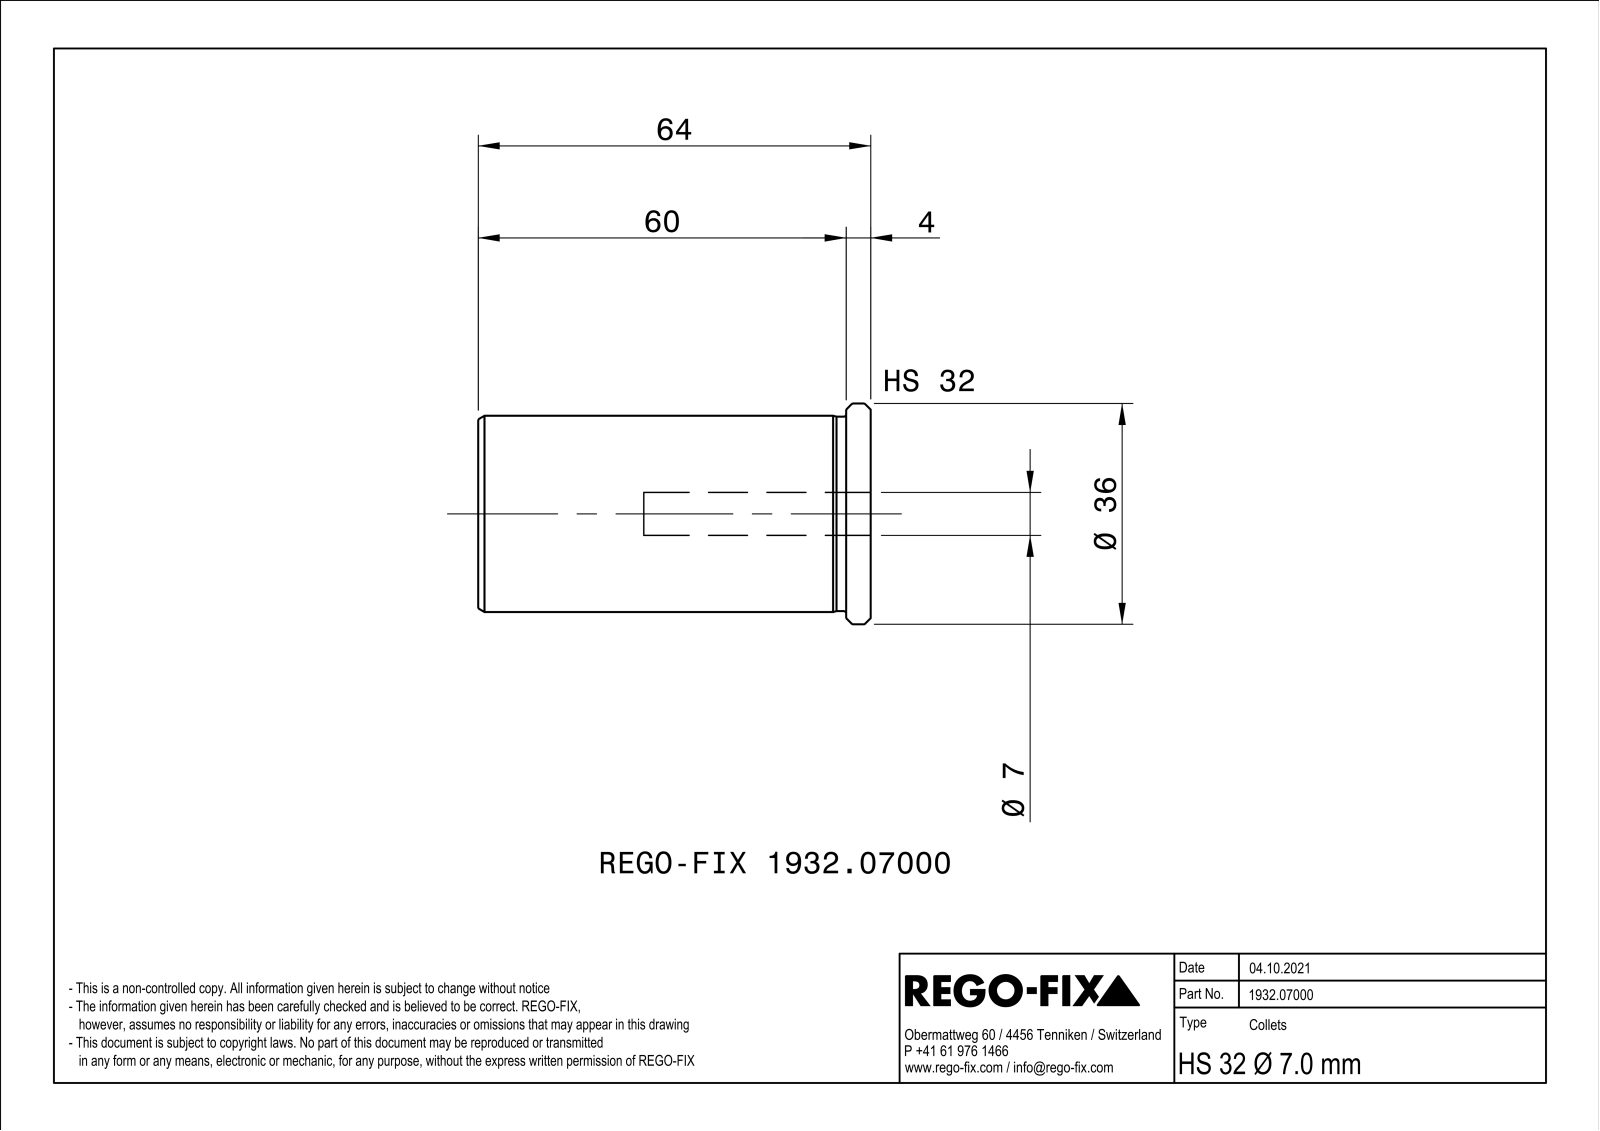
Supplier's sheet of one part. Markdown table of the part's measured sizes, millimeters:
| quantity | value |
| --- | --- |
| part name | NOCUT |
| STEP written by | SIEMENS PLM Software Solid Edge ST10 (AUTOMOTIVE_DESIGN) |
| units | millimeters |
| bodies | 1 solid, 73 faces (14 planar, 12 cylindrical, 47 other) |
| overall size | 64 × 35.99 × 35.99 |
| volume | 39 194 mm³ |
| surface area | 14 414 mm² |
| round holes (diameter × count) | 7 × 1, 10 × 1, 26.5 × 1 |
| round bosses / shafts (diameter × count) | 36 × 1, 32 × 1, 31.7 × 1 |
| main face-to-face distances | 1, 64, 4, 60 |
